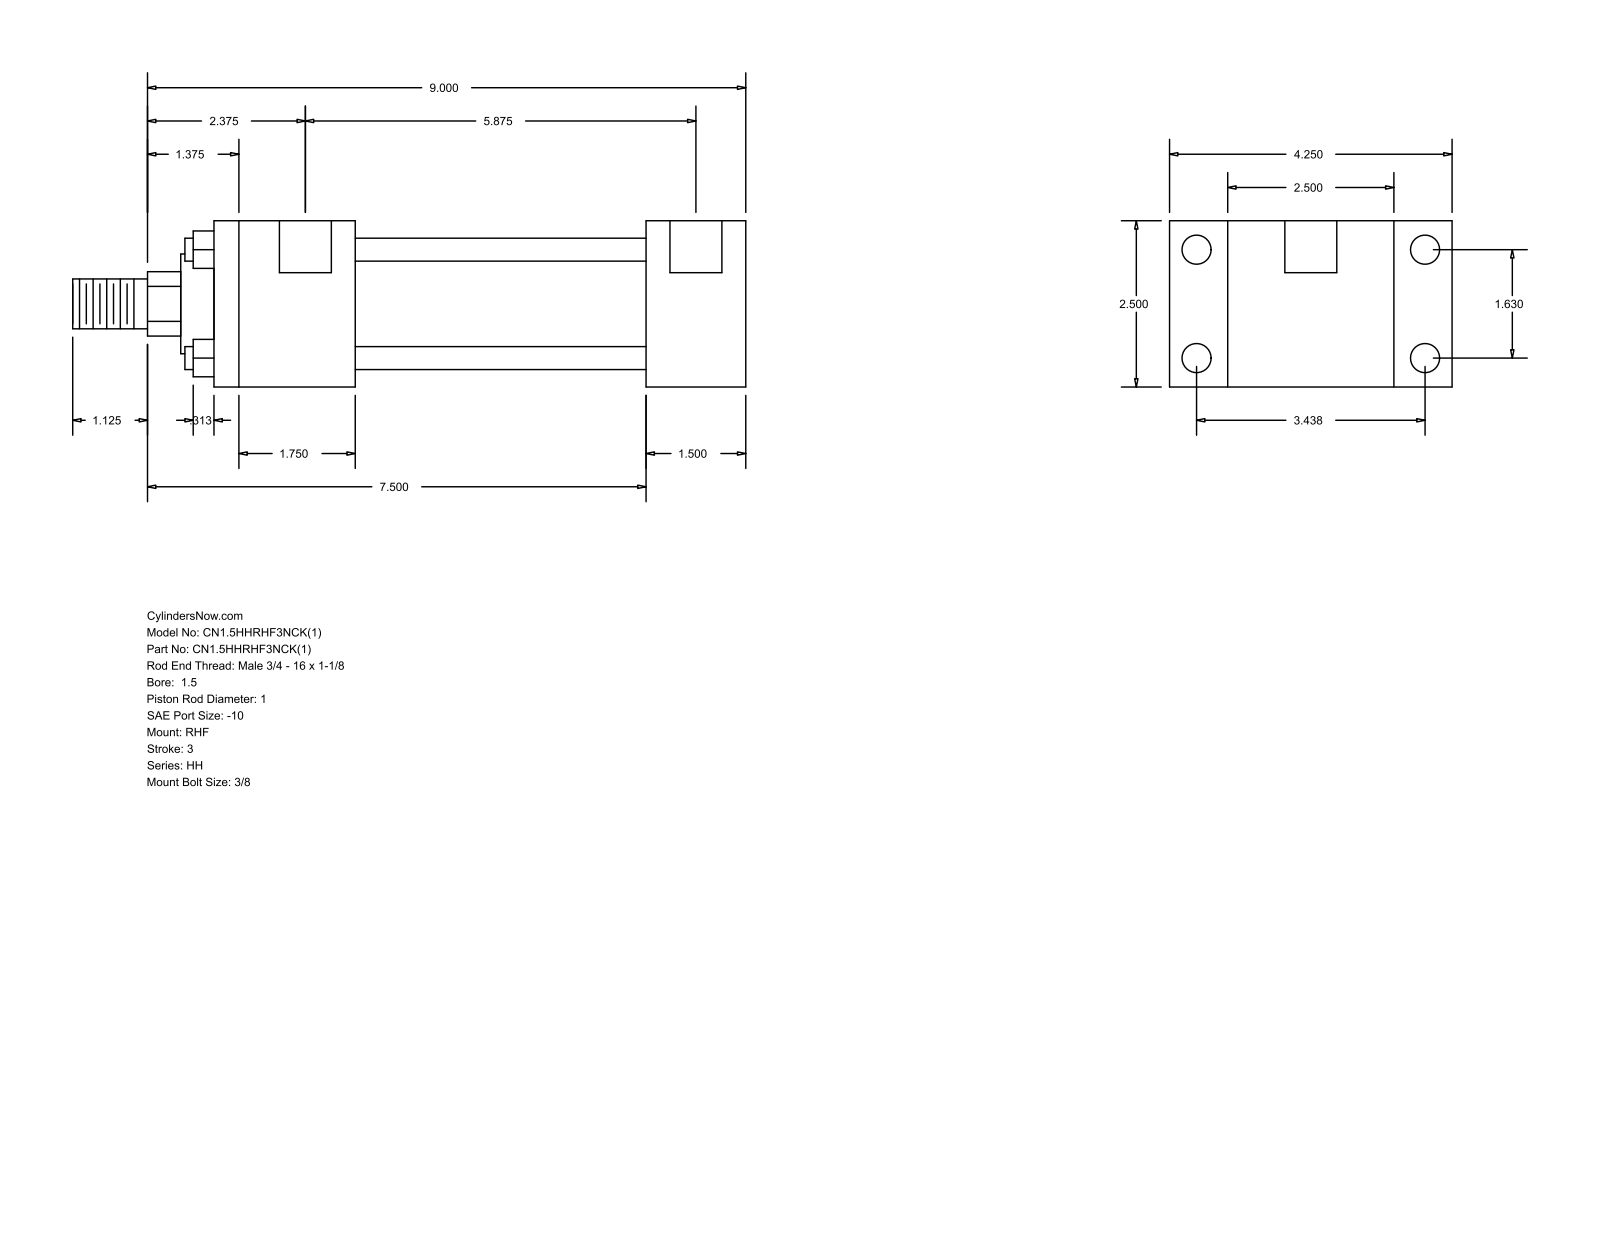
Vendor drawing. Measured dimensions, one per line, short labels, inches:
name: HH_RHF__0150_1
written by: GSSL Pune (CONFIG_CONTROL_DESIGN)
unit: in
bodies: 0 solids, 88 faces (60 planar, 28 cylindrical, 0 other)
size: 10.125 × 4.25 × 2.5
holes: 4× ⌀0.219, 4× ⌀0.438, 2× ⌀0.781
bosses: 4× ⌀0.345, 1× ⌀1.75, 1× ⌀1.5, 1× ⌀1, 1× ⌀0.75
rounds: 1× R0.484
face distances: 2.5, 0.875, 3.375, 1.5, 4.25, 4.375, 5.875, 2.125, 6.5, 8
hole spacings: 0.063, 1.63, 3.438, 3.805, 5.937, 6, 5.875
